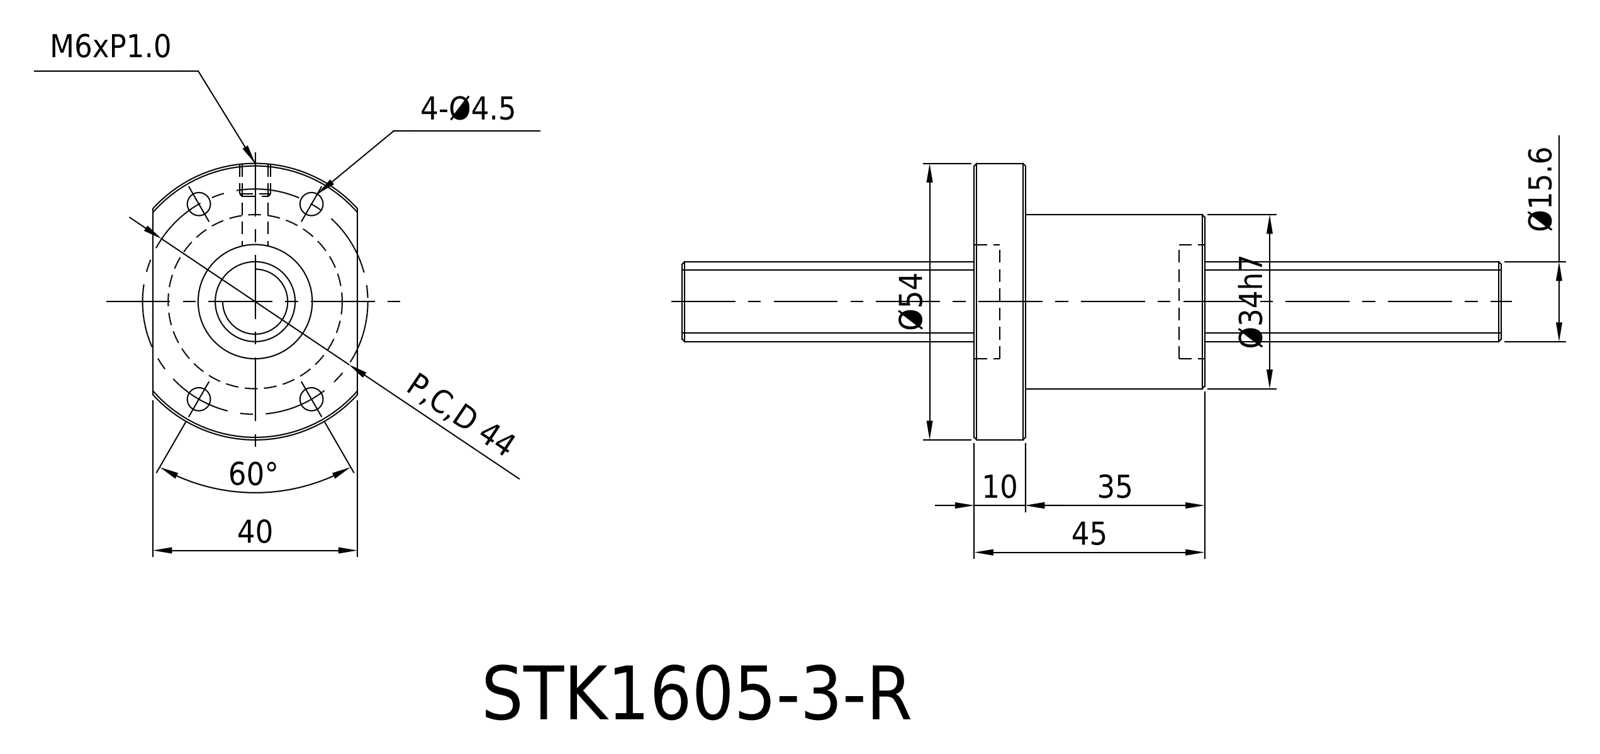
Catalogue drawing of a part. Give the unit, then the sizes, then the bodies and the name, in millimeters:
Units: millimetres
Overall size (bounding box): 54 × 45 × 40
Round holes (diameter × count): ⌀4.5 ×4, ⌀16 ×1
Round bosses / shafts (diameter × count): ⌀34 ×1
Partial cylindrical surfaces — rounded edges, fillets, slot ends (radius × count): R27 ×1
Main face-to-face distances: 10, 35, 45, 40
Hole centre spacings: 19.75, 19.76, 34.2, 39.5
Volume: 41 454 mm³ · Surface area: 11 416 mm²
Bodies: 1 solid, 43 faces (5 planar, 14 cylindrical, 24 other)
Part name (STEP PRODUCT): 1603-STK
STEP written by: CATIA V5 STEP AP214 (AUTOMOTIVE_DESIGN)
